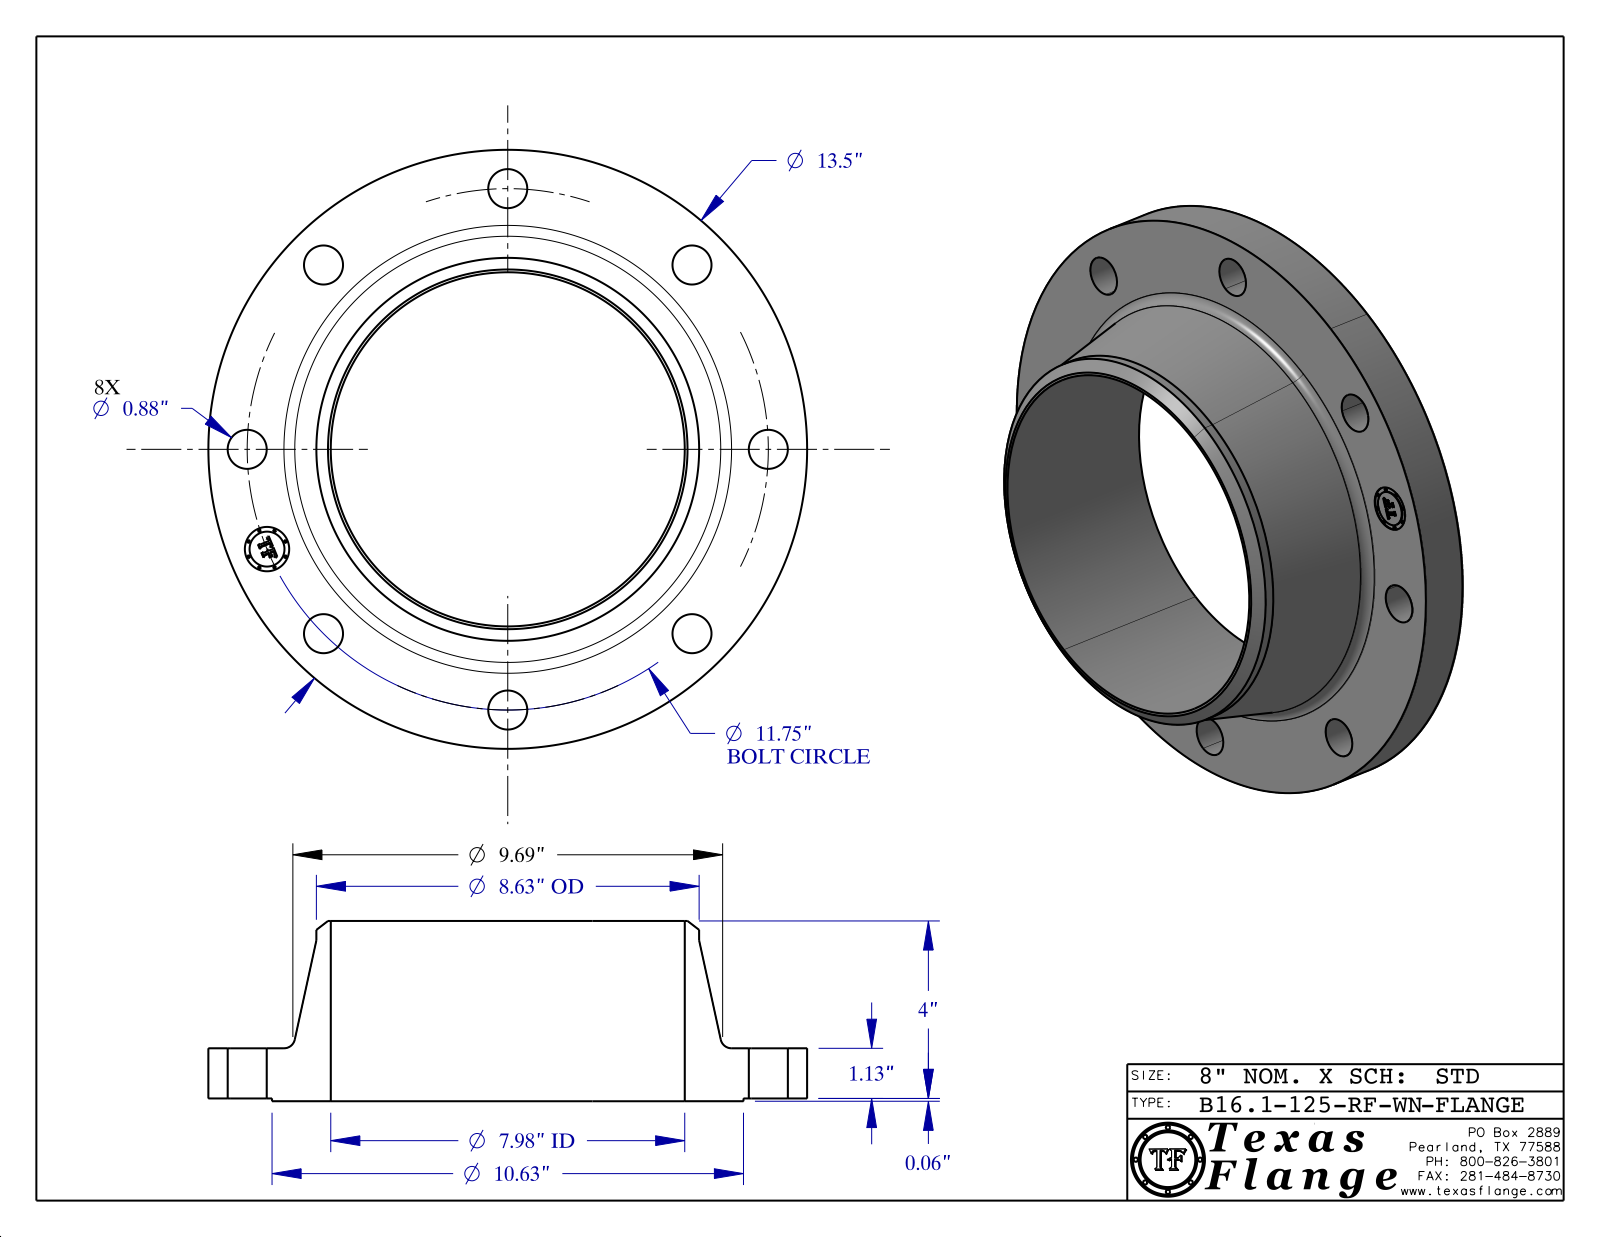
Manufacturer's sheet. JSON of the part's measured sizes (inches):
{"part_name": "B16.1, Class 125-RF-WN", "step_written_by": "CATIA V5 STEP AP214 (AUTOMOTIVE_DESIGN)", "units": "inches", "bodies": {"solids": 1, "faces": 419, "planar": 369, "cylindrical": 44, "other": 6}, "overall_size": [13.5, 13.5, 4.063], "volume_in3": 144.2, "surface_area_in2": 416.2, "round_holes": [[0.88, 8], [1, 1], [7.981, 1]], "round_bosses_or_shafts": [[0.061, 8], [13.5, 1], [10.63, 1], [8.63, 1], [0.788, 1]], "face_to_face_distances": [1.13, 0.063, 1.193, 4.063, 4, 2.87, 1.178, 1.115, 0.015, 2.885], "hole_center_spacings": [5.875, 4.496, 8.309, 10.856, 11.75, 9.77, 2.292, 2.293]}
